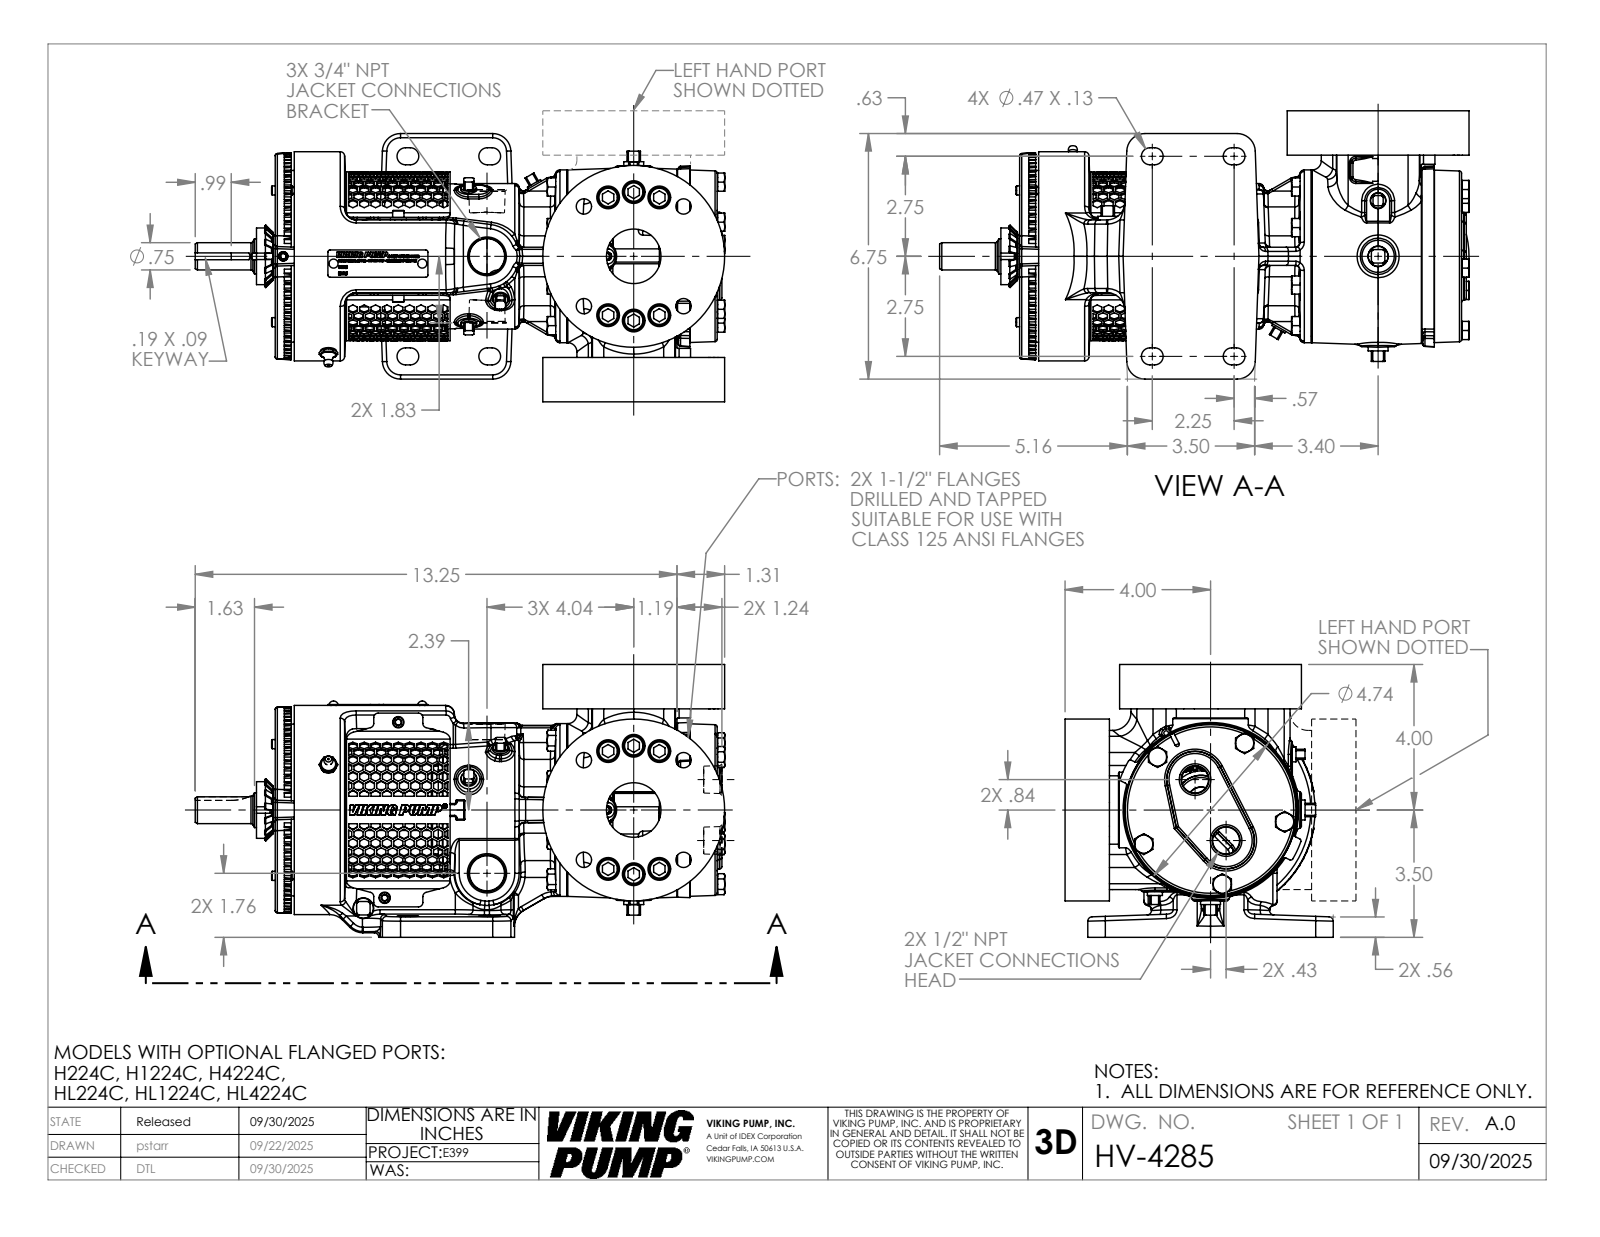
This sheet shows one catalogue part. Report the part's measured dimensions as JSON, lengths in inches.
{"part_name": "HV-4285", "step_written_by": "SolidWorks 2024 (AUTOMOTIVE_DESIGN)", "units": "inches", "bodies": {"solids": 1, "faces": 4363, "planar": 1469, "cylindrical": 880, "other": 2014}, "overall_size": [14.564, 7.5, 7.375], "volume_in3": 250.8, "surface_area_in2": 620.9, "round_holes": [[0.25, 9], [0.625, 9], [0.422, 8], [0.159, 3], [0.197, 3], [0.625, 3], [0.257, 2], [1.5, 2], [0.986, 1], [0.989, 1], [1.265, 1], [4.502, 1]], "round_bosses_or_shafts": [[0.563, 12], [0.5, 5], [0.312, 3], [0.19, 3], [5, 2], [0.25, 2], [5.75, 1], [4.75, 1]], "partial_cylinders_radius": [[0.054, 140], [0.12, 81], [0.06, 55], [0.5, 40], [0.03, 22], [0.25, 10], [0.234, 8], [0.422, 8]], "face_to_face_distances": [1.22, 7.5, 1.94, 12.154, 10.213, 6.28, 1.5, 0.524, 1.417, 11.63], "hole_center_spacings": [1.766, 2.56, 0.711, 0.719, 1.426, 1.937, 2.089, 2.74]}
